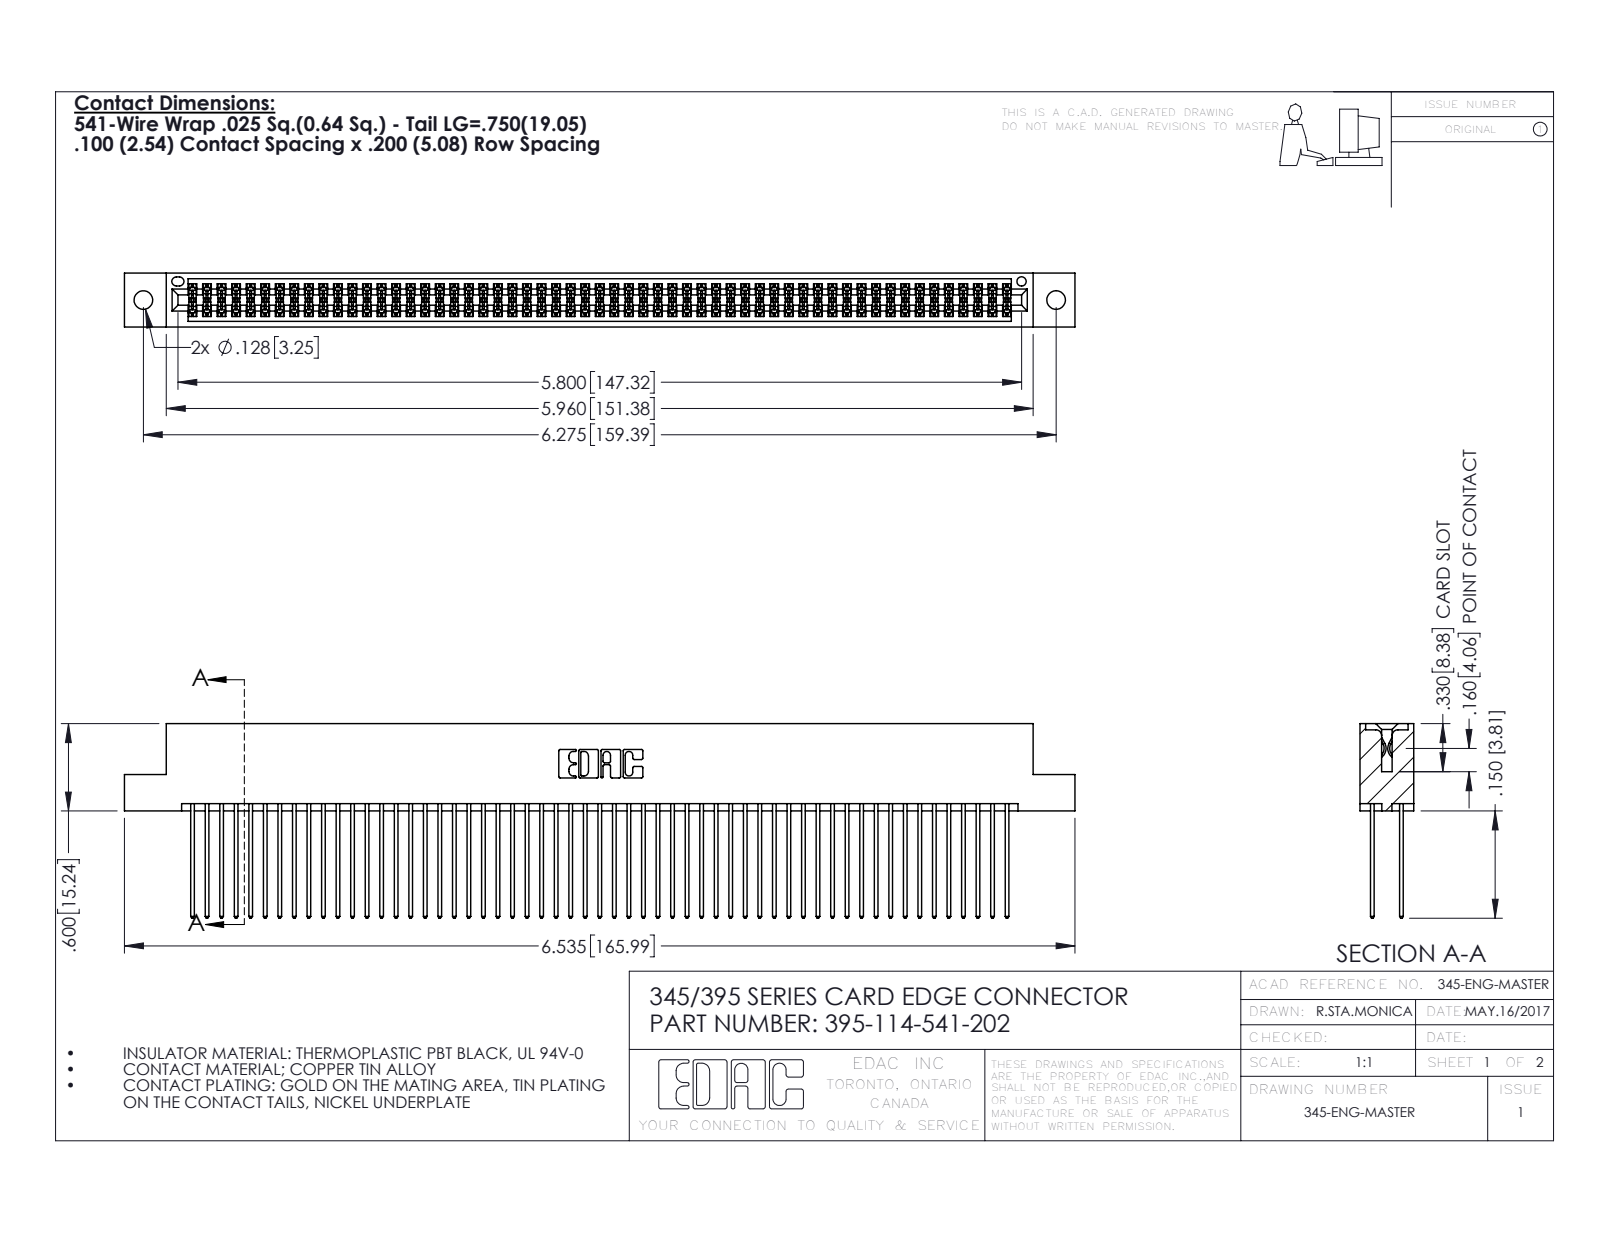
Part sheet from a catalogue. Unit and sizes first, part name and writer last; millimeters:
Units: millimetres
Overall size (bounding box): 166 × 34 × 9.4
Round holes (diameter × count): ⌀3.3 ×2, ⌀1.6 ×1
Partial cylindrical surfaces — rounded edges, fillets, slot ends (radius × count): R0.2 ×171, R0.3 ×114, R0.3 ×22, R0.2 ×6, R0.8 ×6, R0.7 ×3, R0.4 ×2, R0.5 ×2
Main face-to-face distances: 7.6, 1.8, 5.1, 2.5, 6.9, 0.6, 5.7, 9.4, 4.4, 3.8
Hole centre spacings: 6.9, 153.4, 159.4
Volume: 16 880 mm³ · Surface area: 28 050 mm²
Bodies: 115 solids, 5826 faces (3842 planar, 1984 cylindrical, 0 other)
Part name (STEP PRODUCT): 345-292-001_345-293-141; 345 Part_Flush Mounting Lugs - 0.128 Dia; 395-114-541-202
STEP written by: SolidWorks 2016 (CONFIG_CONTROL_DESIGN)
